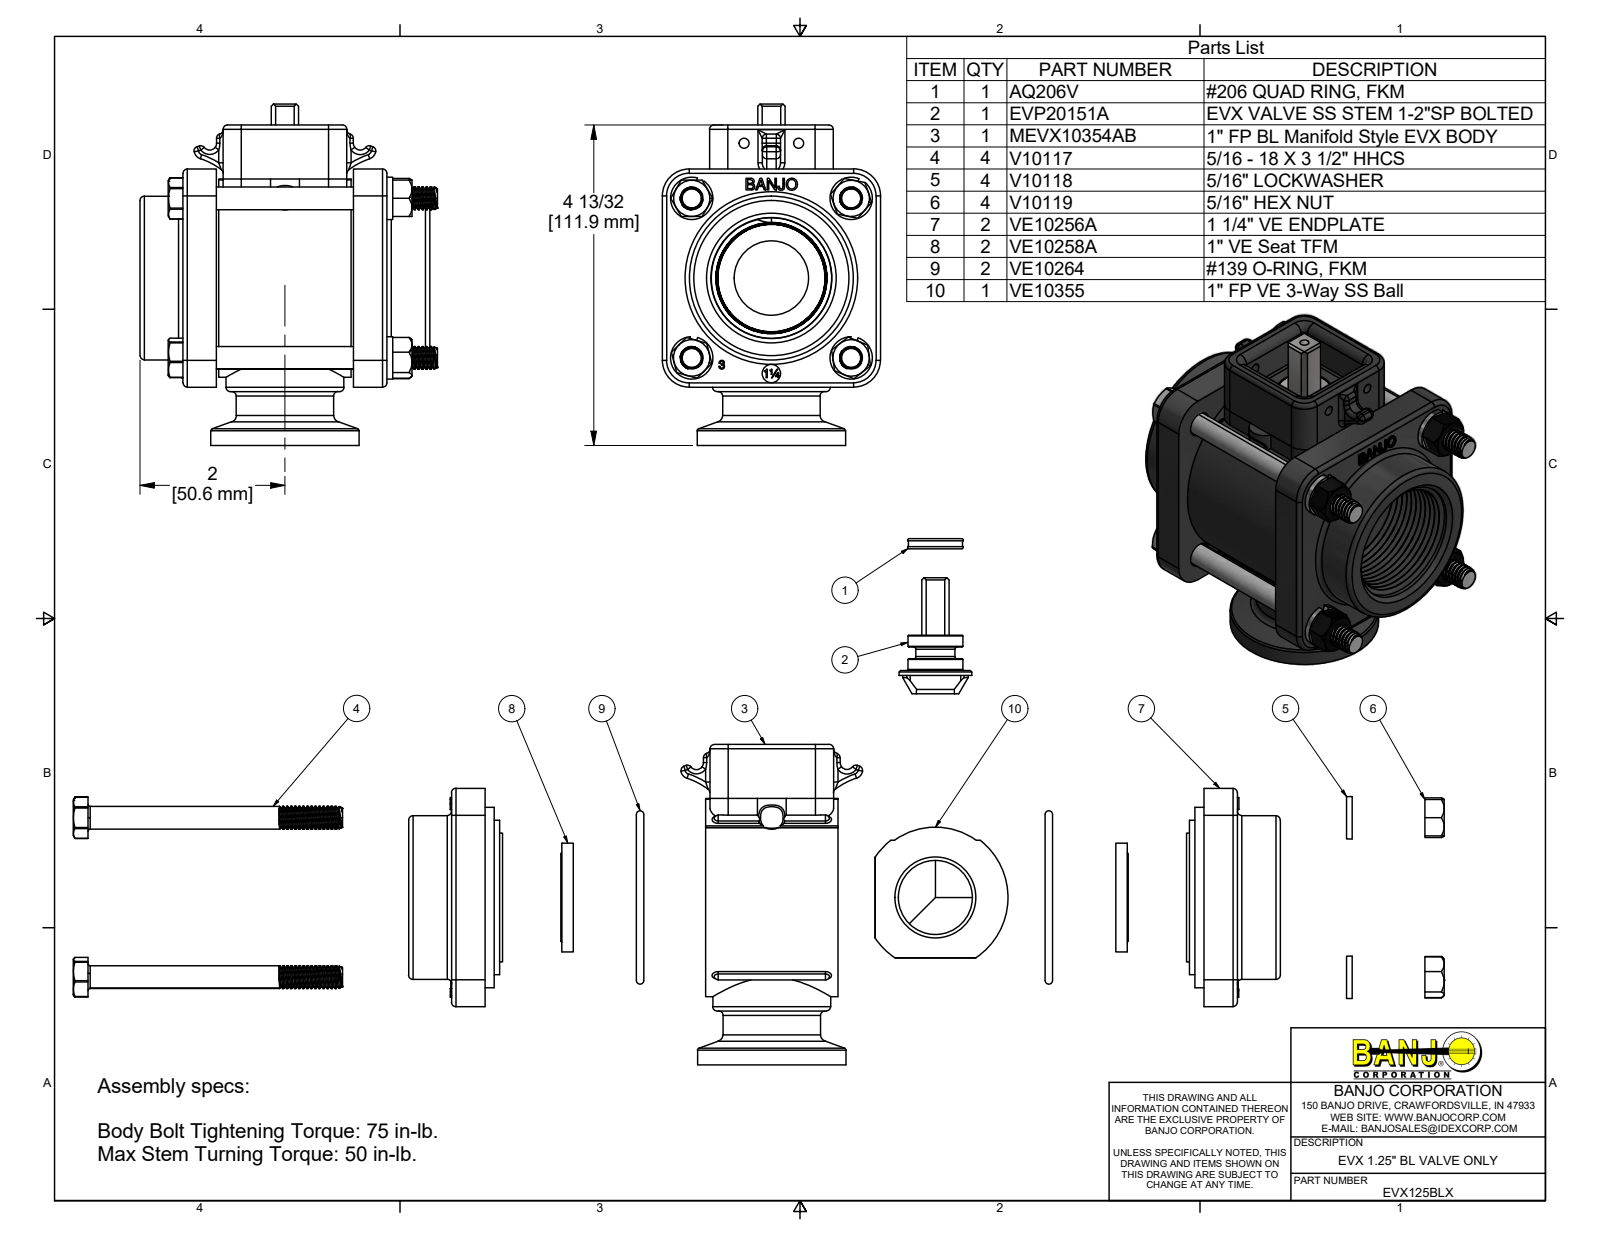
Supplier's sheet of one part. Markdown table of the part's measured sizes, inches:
| quantity | value |
| --- | --- |
| part name | EVX125BLX; AQ206V; EVP20151A; MEVX10354AB (+8 more) |
| STEP written by | Autodesk Inventor 2019 (AUTOMOTIVE_DESIGN) |
| units | inches |
| bodies | 22 solids, 1603 faces (392 planar, 532 cylindrical, 679 other) |
| overall size | 49.551 × 4.693 × 3 |
| volume | 19.79 in³ |
| surface area | 460.2 in² |
| round holes (diameter × count) | 0.252 × 4, 0.322 × 4, 0.35 × 4, 1.02 × 3, 0.135 × 2, 0.25 × 1, 0.76 × 1, 1.38 × 1, 1.5 × 1, 2.12 × 1, 2.375 × 1, 2.5 × 1 |
| round bosses / shafts (diameter × count) | 0.268 × 60, 0.583 × 4, 0.313 × 4, 2.725 × 1, 2.48 × 1, 2.25 × 1, 2.124 × 1, 2.04 × 1 |
| partial cylindrical surfaces (radius × count) | 0.06 × 58, 0.03 × 12, 0.134 × 8, 0.125 × 6, 0.21 × 4, 0.25 × 4, 0.284 × 4, 0.37 × 4 |
| main face-to-face distances | 0.46, 2.345, 2.805, 1.885, 3, 0.125, 0.585, 2.22, 1.76, 1.095 |
| hole center spacings | 1.55, 2.192, 1.046, 1.117, 1.891, 2.646, 3.1, 3.188 |
